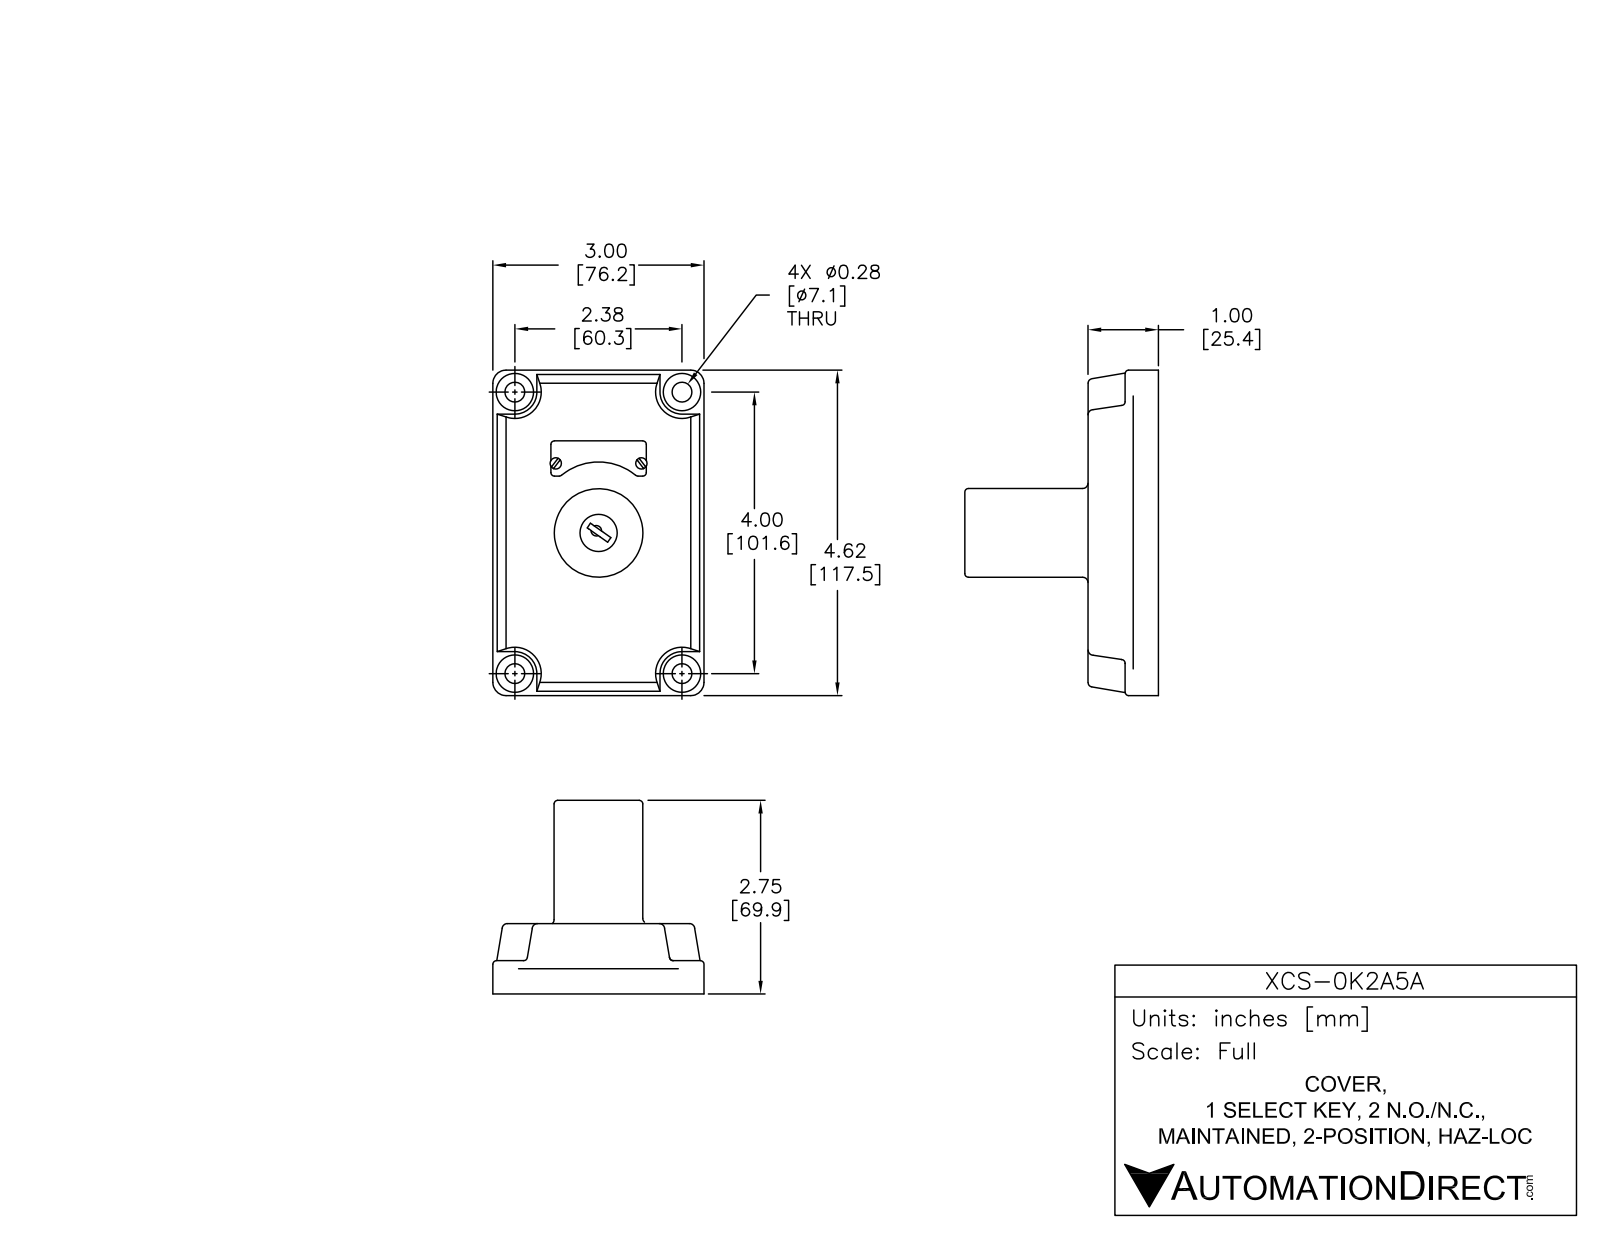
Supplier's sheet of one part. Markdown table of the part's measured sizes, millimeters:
| quantity | value |
| --- | --- |
| part name | XCS-0K2A5A |
| STEP written by | SolidWorks 2015 (AUTOMOTIVE_DESIGN) |
| units | millimeters |
| bodies | 15 solids, 557 faces (236 planar, 186 cylindrical, 135 other) |
| overall size | 139.37 × 119.33 × 78.74 |
| volume | 259 654 mm³ |
| surface area | 69 408 mm² |
| round holes (diameter × count) | 6.86 × 4, 4.99 × 2, 13.5 × 1, 14.5 × 1 |
| round bosses / shafts (diameter × count) | 3.3 × 8, 11.6 × 4, 6.35 × 4, 31.9 × 1, 24 × 1 |
| partial cylindrical surfaces (radius × count) | 0.25 × 28, 1.27 × 10, 0.51 × 8, 1.4 × 8, 2 × 8, 2.54 × 4, 3.5 × 4, 9.65 × 4 |
| main face-to-face distances | 13.34, 12.7, 26.04, 0.63, 0.9, 38.13, 50.83, 64.17, 37.23, 49.93 |
| hole center spacings | 59.11, 60.46, 101.6, 118.23, 17.33 |
